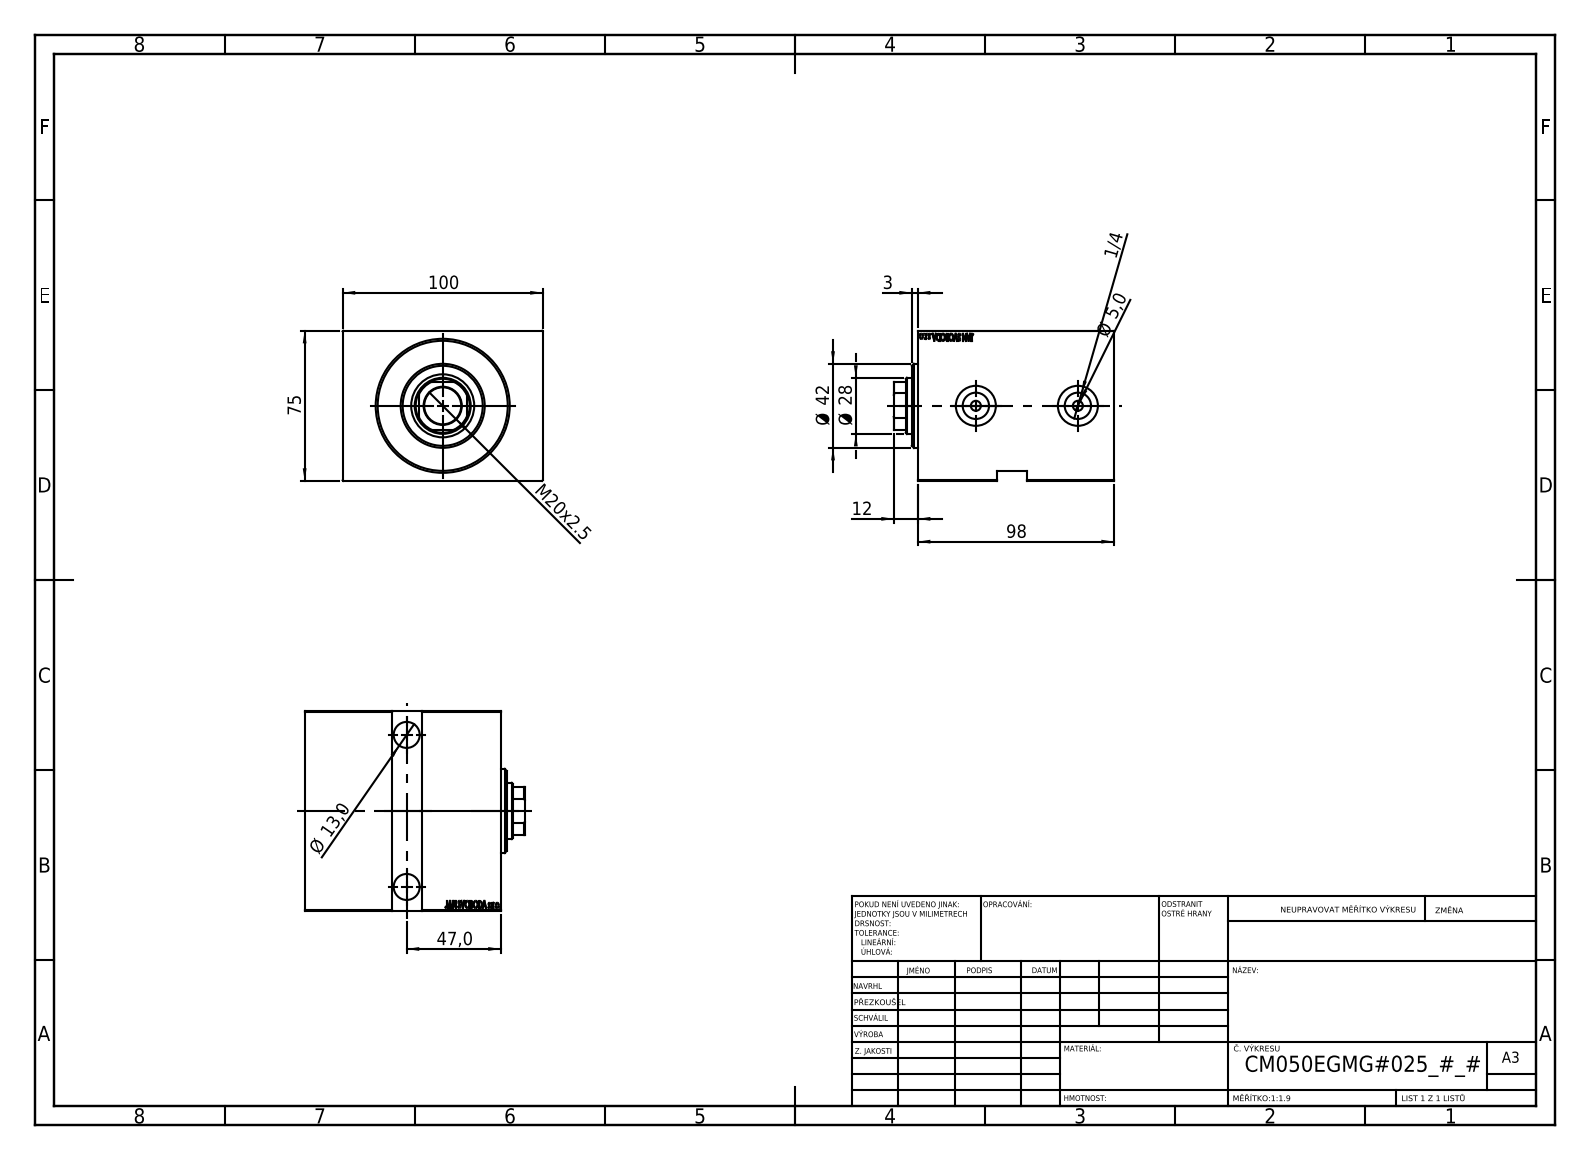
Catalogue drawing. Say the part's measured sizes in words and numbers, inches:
The part is named "V450CM_VC_B; V450CM_E_Body; V450CM_E_VCP". Its 3-D file was written by "SolidWorks 2019 (CONFIG_CONTROL_DESIGN)". It is 3 solids with 848 faces: 410 planar, 44 cylindrical and 394 other. Overall it measures 4.331 by 3.937 by 2.953 inches. Its volume is 41.14 cubic inches and its surface area 152.4 square inches. Round holes: 2 of diameter 0.197, 2 of diameter 0.512, 2 of diameter 0.518, 2 of diameter 0.748, 2 of diameter 0.787, 1 of diameter 0.728, 1 of diameter 1.102, 1 of diameter 1.24, 1 of diameter 1.969, 1 of diameter 2.559. Round bosses or shafts: 1 of diameter 2.047, 1 of diameter 1.654. Partial cylindrical surfaces (rounded edges, fillets, slot ends): 1 of radius 0.531. The main face-to-face distances are 2.953, 3.937, 3.858, 0.551, 3.307, 0.197, 3.661, 3.11, 3.205, 2.654. The hole center spacings are 2.008, 2.992.
